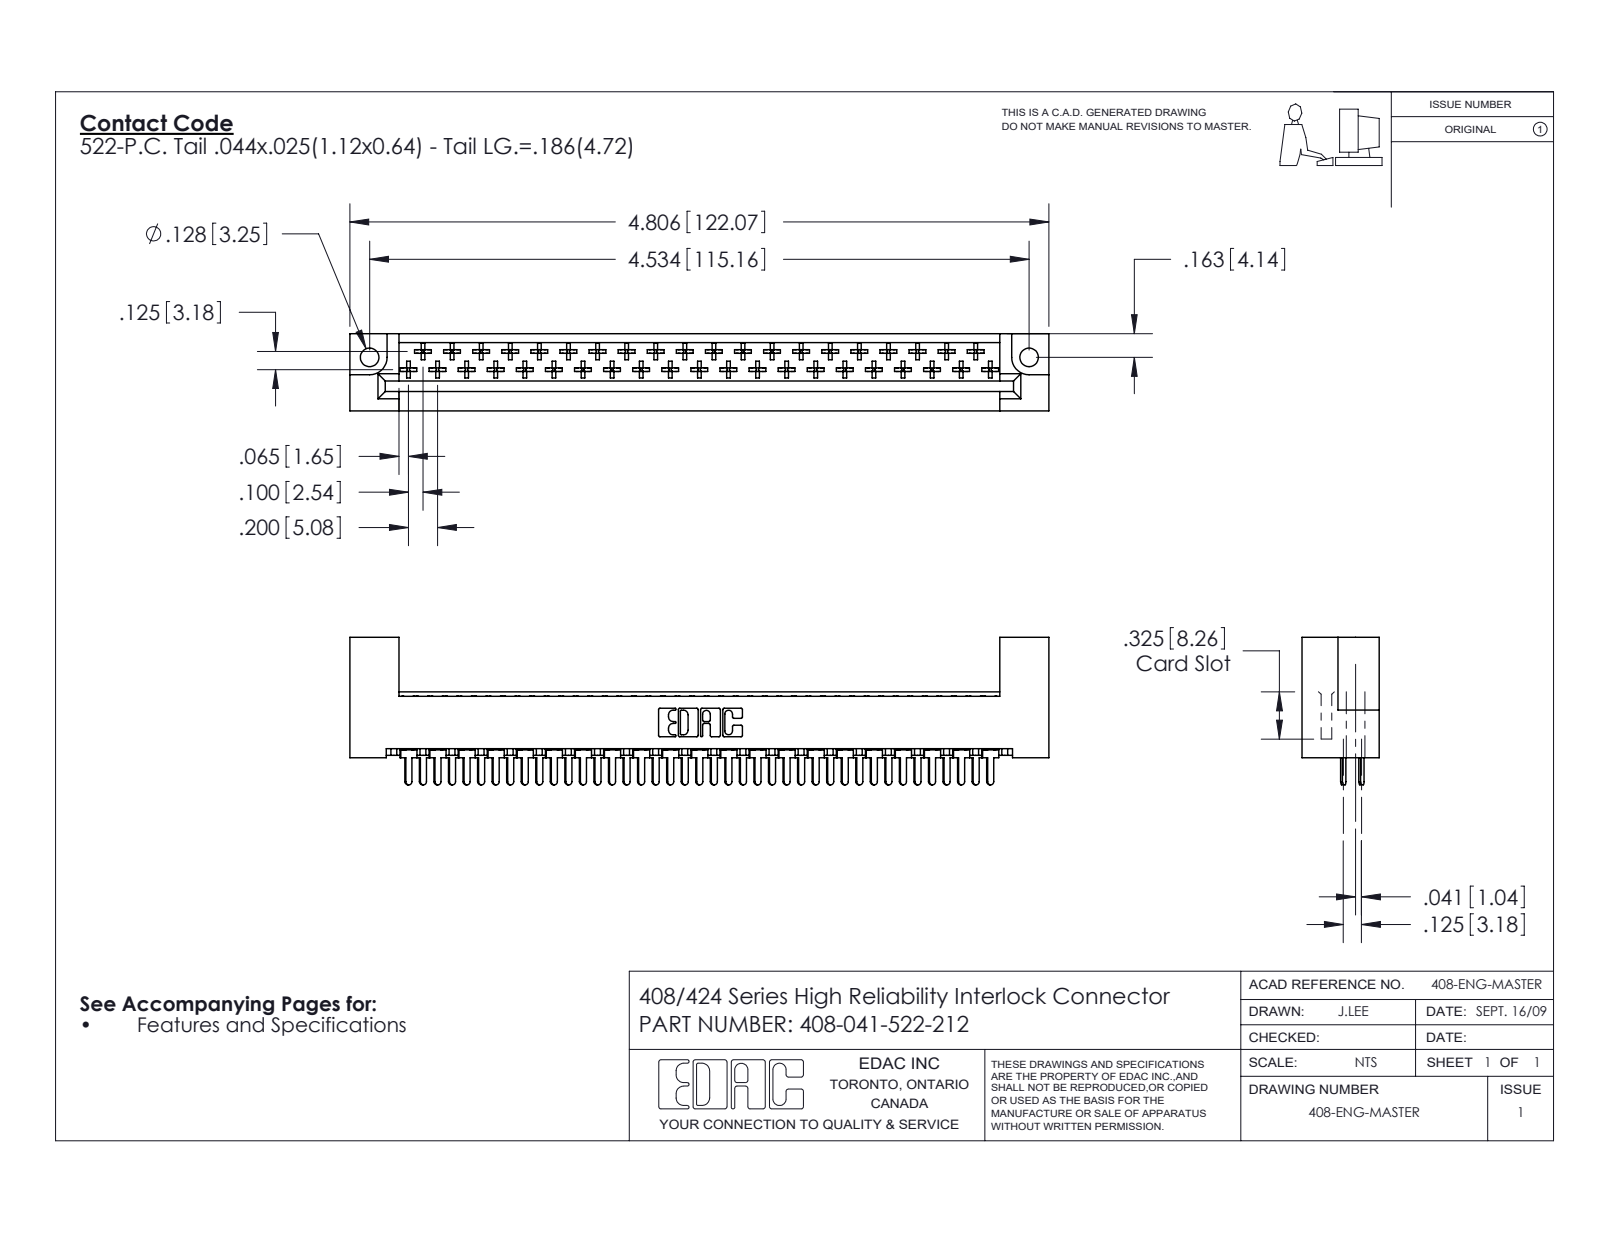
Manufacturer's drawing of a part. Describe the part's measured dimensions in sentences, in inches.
The part is named "408-047-522-212; 408-290-001_408-290-122; 408 Part_041 - 2". Its 3-D file was written by "SolidWorks 2016 (CONFIG_CONTROL_DESIGN)". It is 42 solids with 2394 faces: 1811 planar, 419 cylindrical and 164 other. Overall it measures 4.806 by 1.014 by 0.531 inches. Its volume is 0.919 cubic inches and its surface area 27.49 square inches. Round holes: 2 of diameter 0.128. Partial cylindrical surfaces (rounded edges, fillets, slot ends): 246 of radius 0.01, 43 of radius 0.02, 41 of radius 0.022, 22 of radius 0.01, 6 of radius 0.007, 6 of radius 0.031, 3 of radius 0.026, 2 of radius 0.12. The main face-to-face distances are 0.531, 0.125, 0.1, 0.025, 0.025, 0.361, 0.235, 0.259, 0.398, 0.217. The hole center spacings are 4.534.
